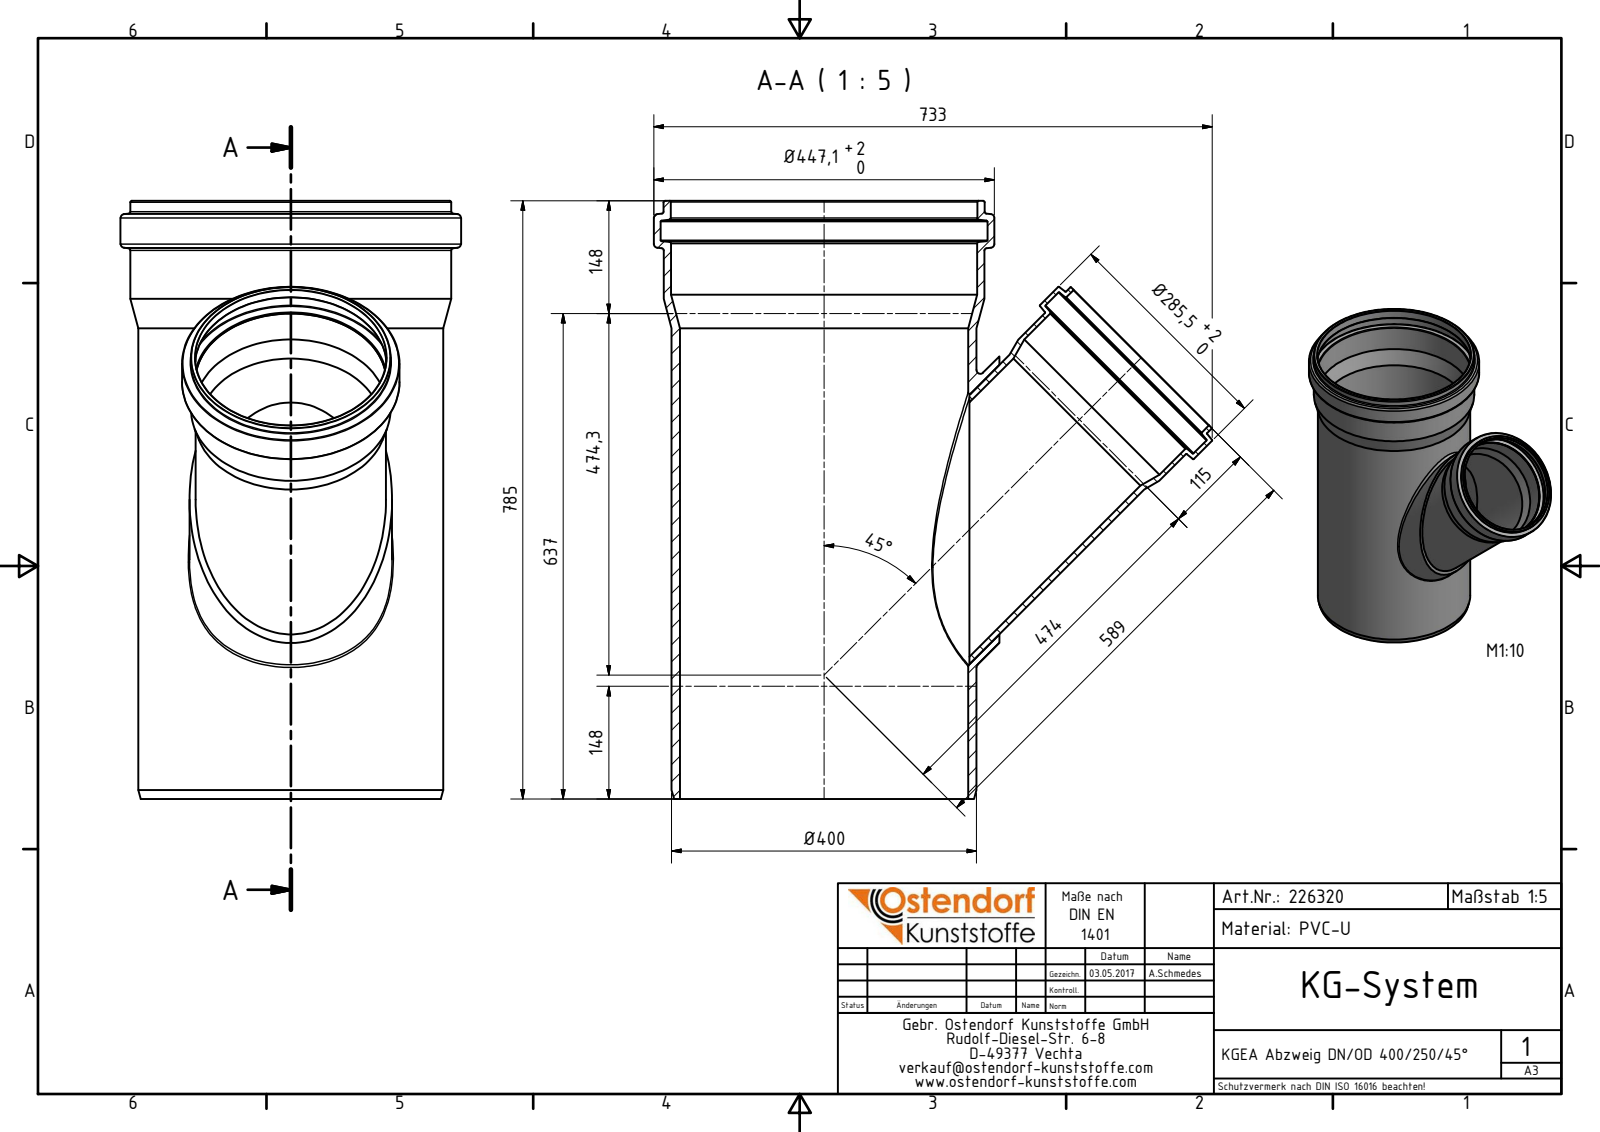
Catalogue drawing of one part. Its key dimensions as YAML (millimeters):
part_name: "226320 KGEA Abzweig DN_OD 400_250_45°; 226320 KGEA Abzweig DN_OD 400_250_45° Abzweig"
step_written_by: "Autodesk Inventor 2016 (AUTOMOTIVE_DESIGN)"
units: millimeters
bodies: {solids: 2, faces: 60, planar: 6, cylindrical: 19, other: 35}
overall_size: [785, 733, 447.1]
volume: 12120000
surface_area: 2554000
round_holes:
  - {diameter: 251.1, count: 2}
  - {diameter: 235.8, count: 1}
  - {diameter: 250, count: 1}
  - {diameter: 250.8, count: 1}
  - {diameter: 274.5, count: 1}
  - {diameter: 378.35, count: 1}
  - {diameter: 402, count: 1}
  - {diameter: 402.4, count: 1}
  - {diameter: 429.1, count: 1}
round_bosses_or_shafts:
  - {diameter: 447.1, count: 1}
  - {diameter: 421.4, count: 1}
  - {diameter: 421.1, count: 1}
  - {diameter: 400.35, count: 1}
  - {diameter: 285.5, count: 1}
  - {diameter: 266, count: 1}
  - {diameter: 262.1, count: 1}
  - {diameter: 261.8, count: 1}
face_to_face_distances: [785, 39.23, 43.63]
